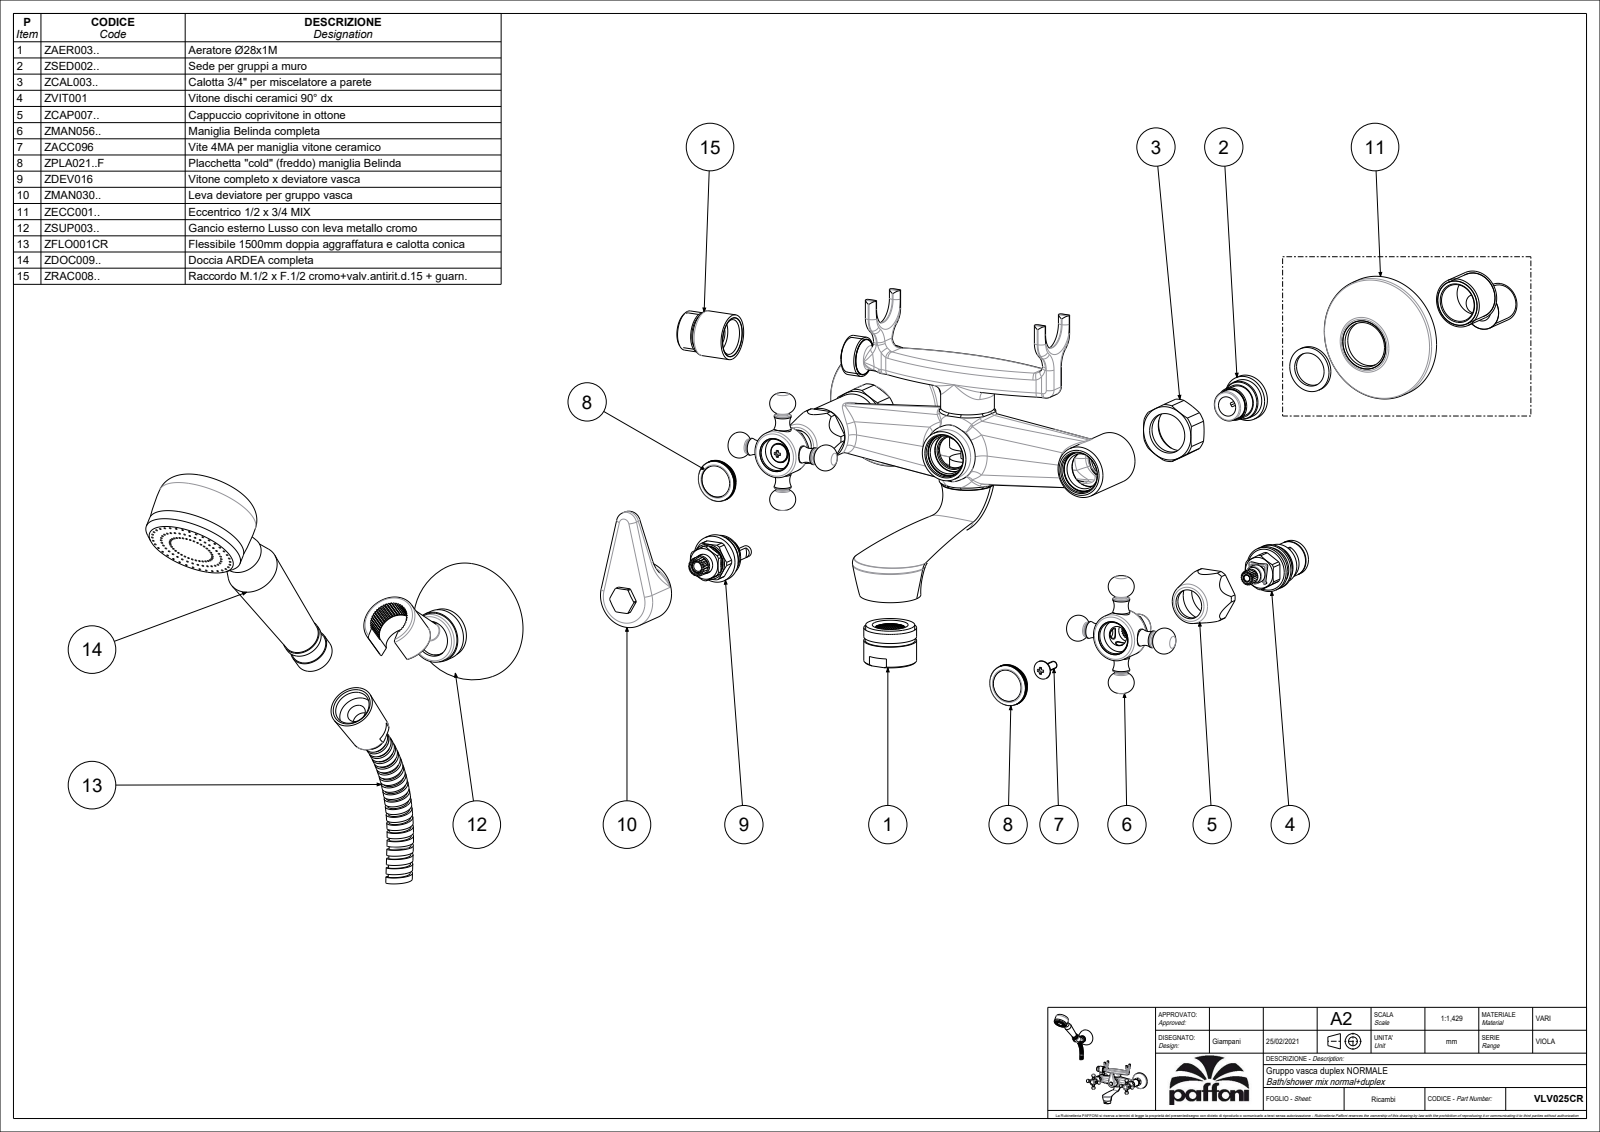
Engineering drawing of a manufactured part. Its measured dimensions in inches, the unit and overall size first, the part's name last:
Units: inches
Overall size (bounding box): 14.599 × 12.687 × 9.186
Round holes (diameter × count): ⌀0.669 ×2, ⌀0.748 ×2, ⌀0.846 ×2, ⌀0.276 ×1, ⌀0.575 ×1, ⌀0.591 ×1, ⌀0.598 ×1, ⌀0.606 ×1, ⌀0.677 ×1, ⌀0.732 ×1, ⌀0.807 ×1, ⌀0.886 ×1
Round bosses / shafts (diameter × count): ⌀0.354 ×3, ⌀0.276 ×3, ⌀2.579 ×2, ⌀1.083 ×2, ⌀0.984 ×2, ⌀0.551 ×2, ⌀0.512 ×2, ⌀2.106 ×1
Partial cylindrical surfaces — rounded edges, fillets, slot ends (radius × count): R0.118 ×22, R0.039 ×7, R0.394 ×7, R0.059 ×4, R0.197 ×4, R0.236 ×3, R0.404 ×3, R0.61 ×3
Main face-to-face distances: 0.118, 0.394, 1.516, 1.339, 0.276, 0.512, 2.854, 1.142, 0.906, 4.252
Hole centre spacings: 3.11, 3.228, 6.22
Volume: 32.91 in³ · Surface area: 248.6 in²
Bodies: 5 solids, 1836 faces (589 planar, 480 cylindrical, 767 other)
Part name (STEP PRODUCT): VLV025CR
STEP written by: CREO PARAMETRIC BY PTC INC, 2020044 (CONFIG_CONTROL_DESIGN)
